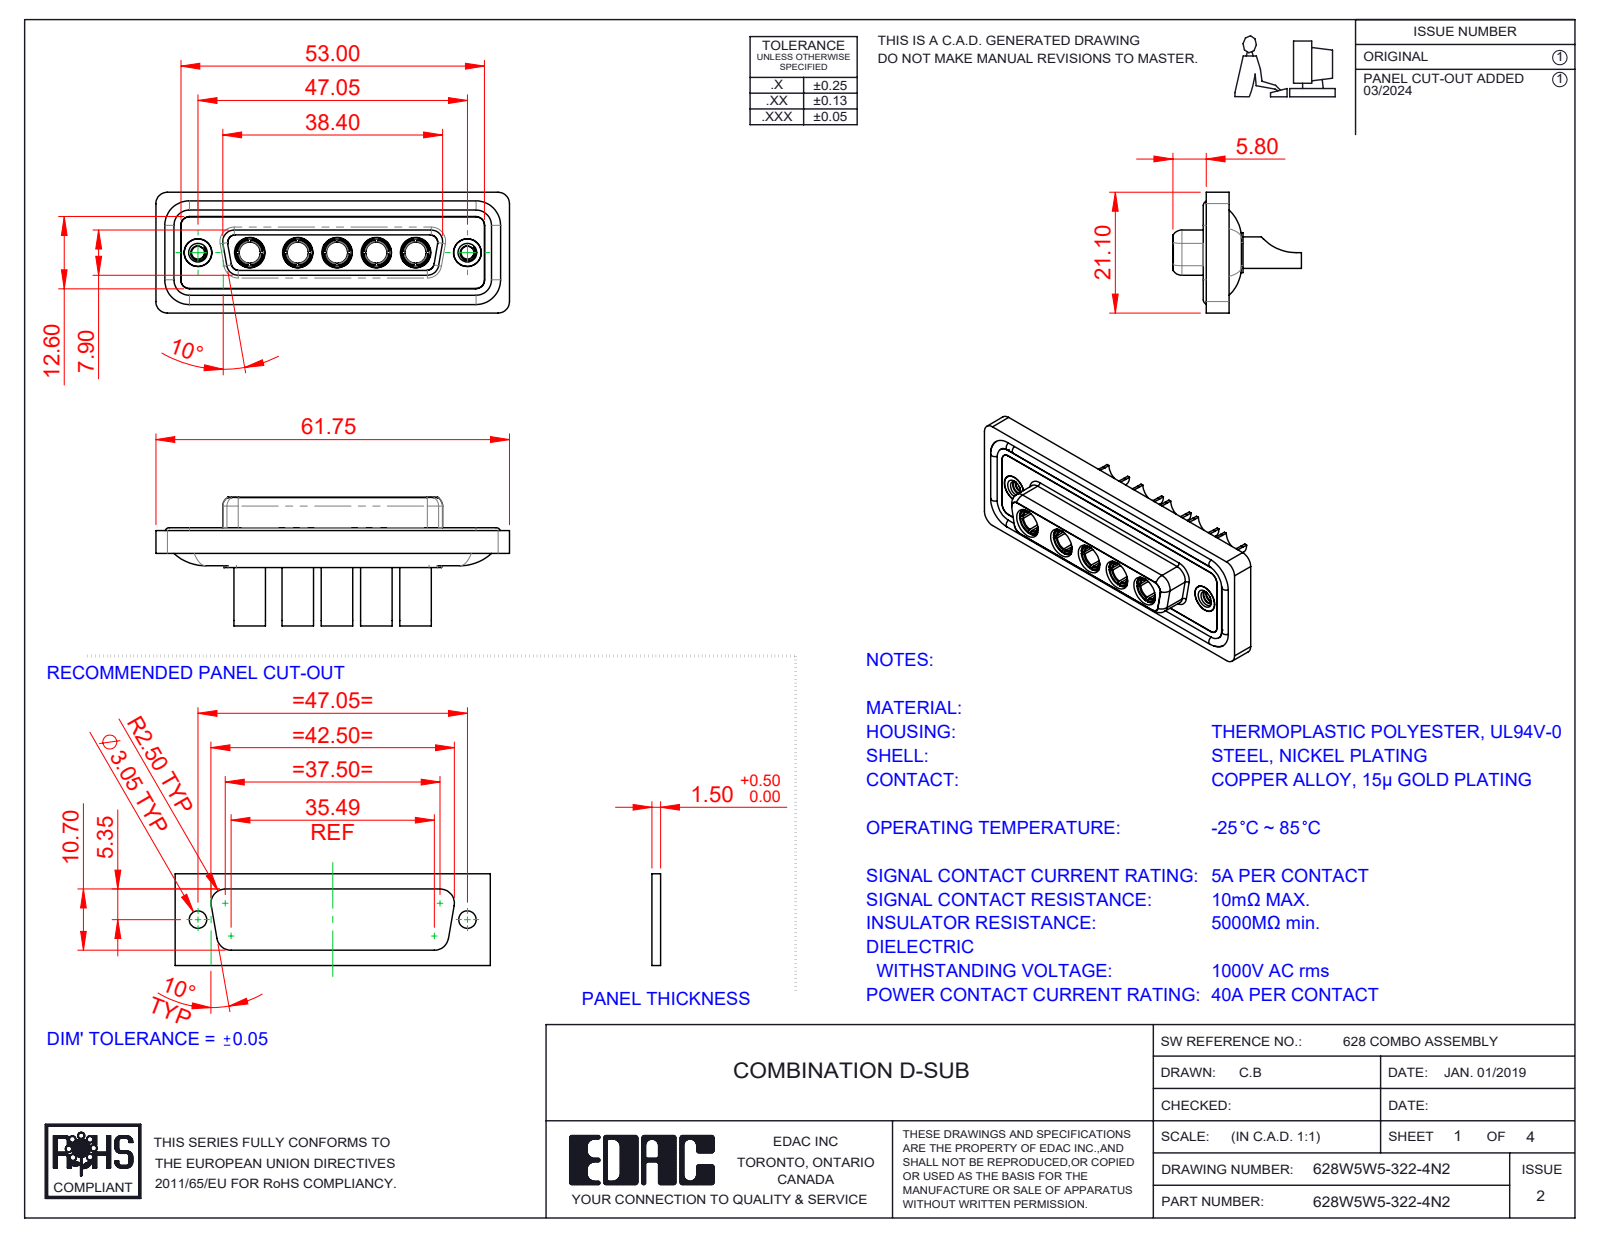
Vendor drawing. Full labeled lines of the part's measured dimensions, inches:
Part name (STEP PRODUCT): 628Combo Shell Front_25 Contacts; 628Combo Housing_5W5; 628Combo Threaded Rivet_2; 628W5W5-322-4N2 (+3 more)
STEP written by: SolidWorks 2023 (CONFIG_CONTROL_DESIGN)
Units: inches
Bodies: 17 solids, 771 faces (260 planar, 308 cylindrical, 203 other)
Overall size (bounding box): 2.431 × 0.884 × 0.831
Volume: 0.511 in³ · Surface area: 21.88 in²
Round holes (diameter × count): ⌀0.191 ×7, ⌀0.146 ×5, ⌀0.181 ×5, ⌀0.209 ×5, ⌀0.089 ×2, ⌀0.157 ×2, ⌀0.159 ×2, ⌀0.197 ×2
Round bosses / shafts (diameter × count): ⌀0.217 ×5, ⌀0.205 ×5, ⌀0.195 ×5, ⌀0.187 ×5, ⌀0.148 ×5, ⌀0.063 ×4, ⌀0.195 ×2, ⌀0.189 ×2
Partial cylindrical surfaces — rounded edges, fillets, slot ends (radius × count): R0.059 ×22, R0.079 ×18, R0.053 ×8, R0.063 ×8, R0.083 ×5, R0.01 ×4, R0.02 ×4, R0.024 ×4
Main face-to-face distances: 0.016, 0.293, 0.071, 0.222, 0.02, 0.278, 0.26, 0.063, 0.043, 0.114
Hole centre spacings: 0.27, 0.356, 0.54, 1.496, 0.33, 0.6, 0.626, 0.686
